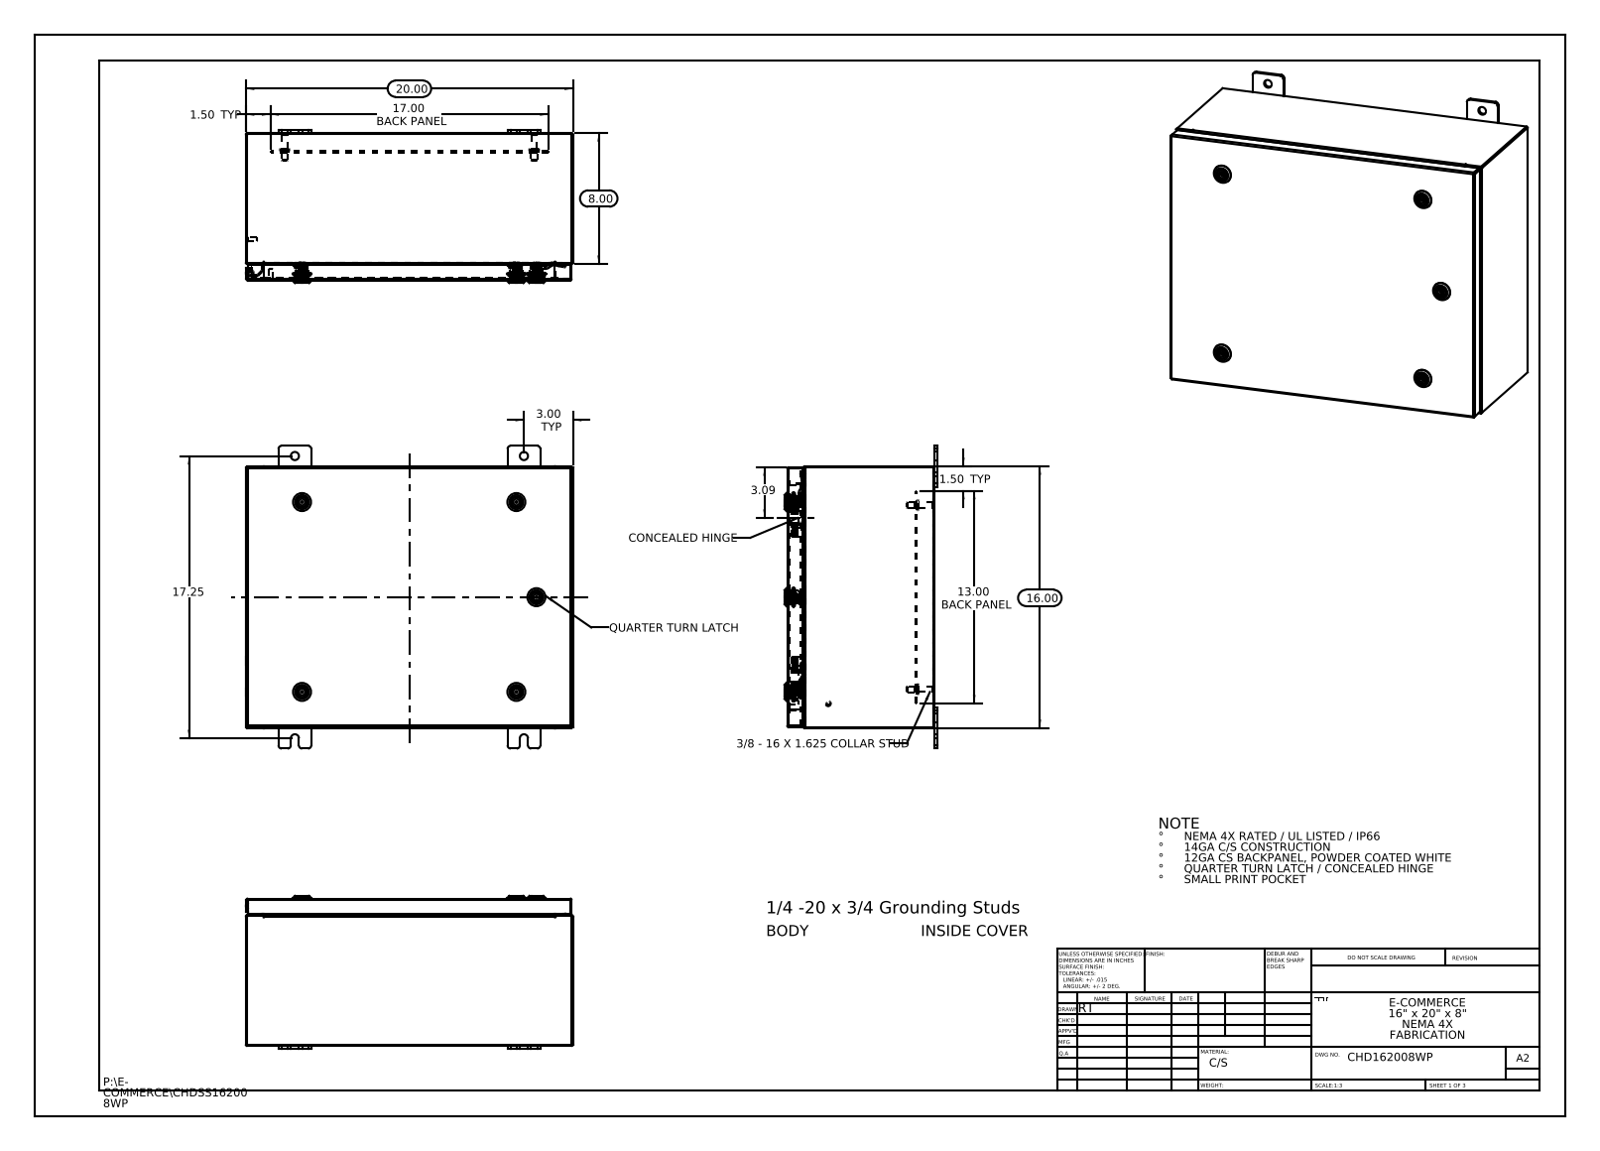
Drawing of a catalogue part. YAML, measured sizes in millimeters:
part_name: "CHDSS162008WP Top; Nut-211301-IB-Industrilas_Nut-211301-IB-Industrilas; Insert-221320-IB-Industrilas_Insert-221320-IB-Industrilas; Concealed Hinge enclosure side (+8 more)"
step_written_by: "SolidWorks 2013 (CONFIG_CONTROL_DESIGN)"
units: millimeters
bodies: {solids: 49, faces: 4592, planar: 1366, cylindrical: 1436, other: 1790}
overall_size: [508, 469.9, 237.6]
volume: 2211000
surface_area: 2194000
round_holes:
  - {diameter: 12.7, count: 8}
  - {diameter: 5, count: 5}
  - {diameter: 10, count: 5}
  - {diameter: 10.2, count: 5}
  - {diameter: 16, count: 5}
  - {diameter: 20, count: 5}
  - {diameter: 3.5, count: 4}
  - {diameter: 5.4, count: 2}
round_bosses_or_shafts:
  - {diameter: 6, count: 7}
  - {diameter: 28, count: 5}
  - {diameter: 19.8, count: 5}
  - {diameter: 15.9, count: 5}
  - {diameter: 15.5, count: 5}
  - {diameter: 13.5, count: 5}
  - {diameter: 10, count: 5}
  - {diameter: 2.9, count: 5}
partial_cylinders:
  - {radius: 0.2, count: 165}
  - {radius: 3, count: 165}
  - {radius: 0.7, count: 60}
  - {radius: 4.8, count: 24}
  - {radius: 0.5, count: 20}
  - {radius: 5, count: 20}
  - {radius: 0.3, count: 18}
  - {radius: 2.2, count: 18}
face_to_face_distances: [1.9, 1.9, 404.5, 228.9, 226.9, 227, 225.1, 506.1, 25.4, 27.3]
hole_center_spacings: [47.2, 77.9, 142.9, 285.8, 294.6, 330.6, 332.7, 355.6]
